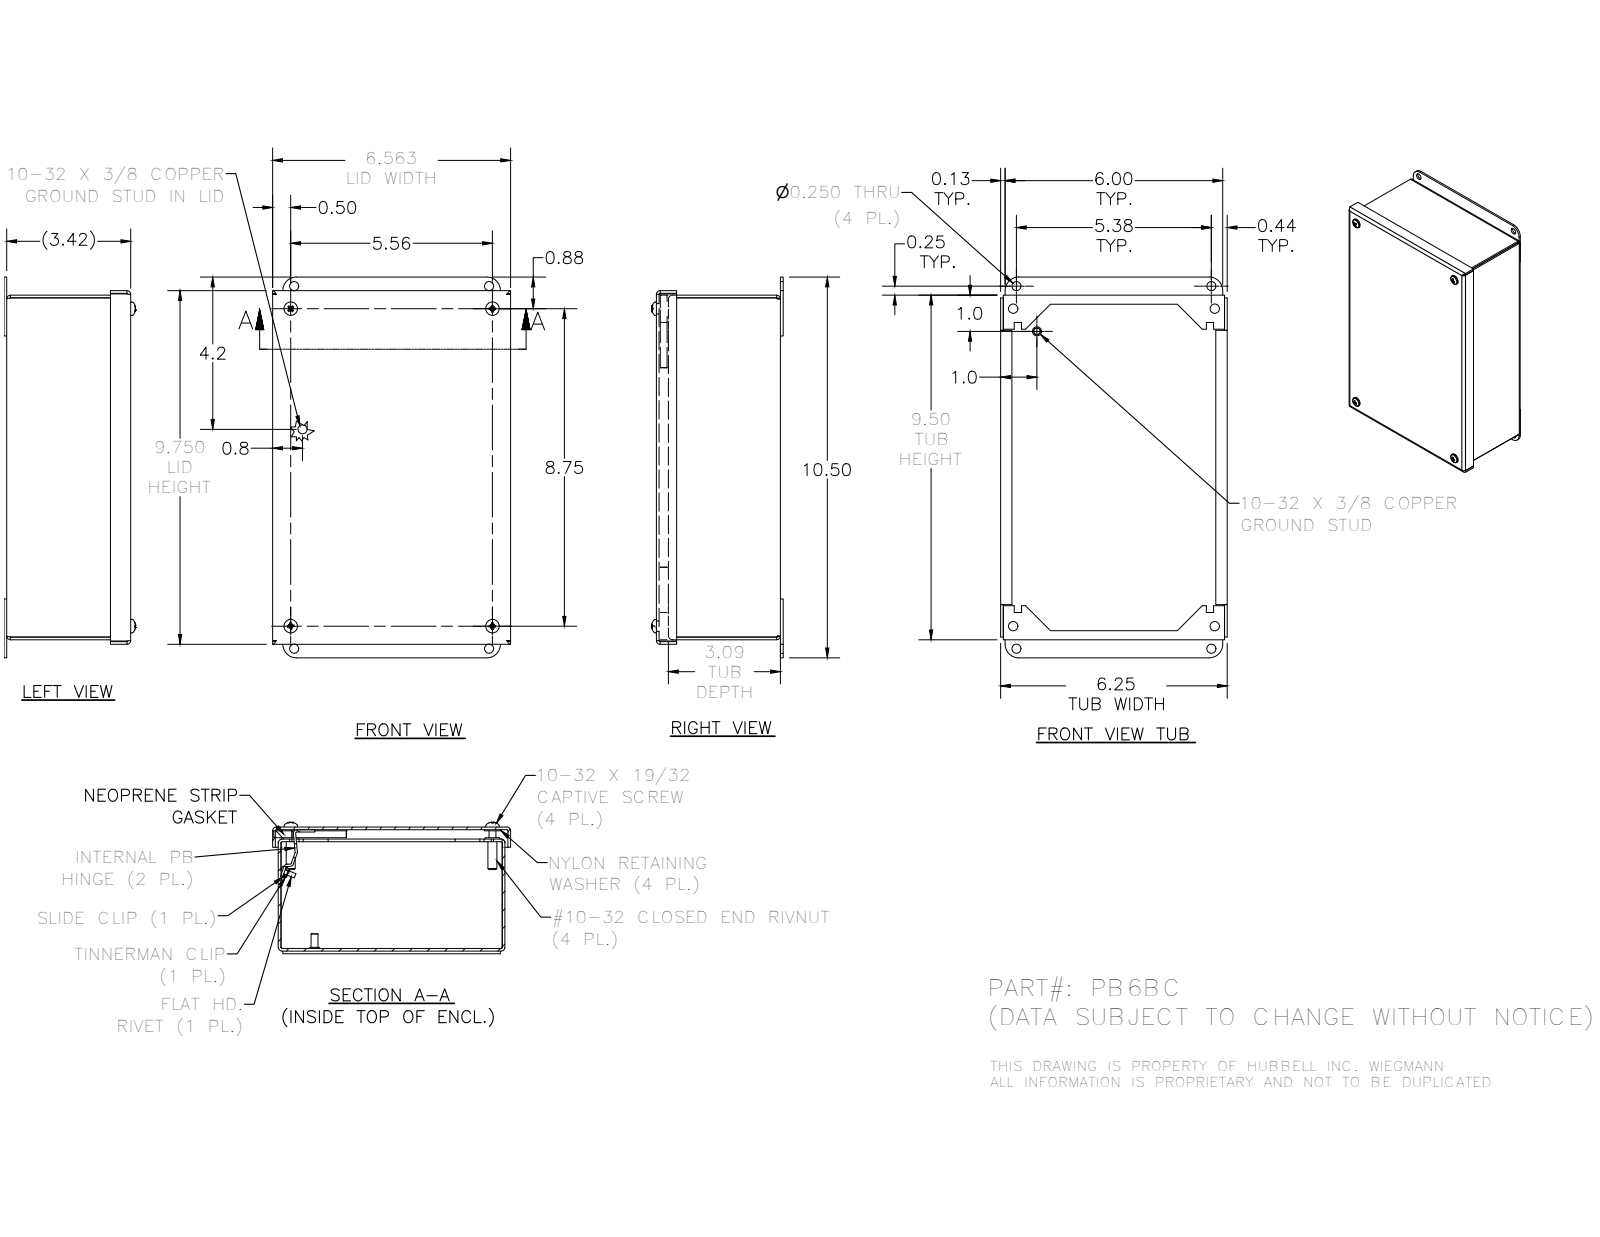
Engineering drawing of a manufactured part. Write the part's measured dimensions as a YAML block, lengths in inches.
part_name: "3285; 39077; 316243; 31817 (+8 more)"
step_written_by: "Autodesk Inventor 2016 (AUTOMOTIVE_DESIGN)"
units: inches
bodies: {solids: 25, faces: 599, planar: 355, cylindrical: 130, other: 114}
overall_size: [10.5, 6.563, 3.626]
volume: 20.27
surface_area: 554.6
round_holes:
  - {diameter: 0.156, count: 4}
  - {diameter: 0.196, count: 4}
  - {diameter: 0.25, count: 4}
  - {diameter: 0.257, count: 4}
  - {diameter: 0.278, count: 4}
  - {diameter: 0.281, count: 4}
  - {diameter: 0.14, count: 2}
  - {diameter: 0.313, count: 2}
round_bosses_or_shafts:
  - {diameter: 0.19, count: 6}
  - {diameter: 0.453, count: 4}
  - {diameter: 0.406, count: 4}
  - {diameter: 0.373, count: 4}
  - {diameter: 0.248, count: 4}
  - {diameter: 0.25, count: 3}
  - {diameter: 0.125, count: 1}
partial_cylinders:
  - {radius: 0.031, count: 12}
  - {radius: 0.105, count: 12}
  - {radius: 0.188, count: 6}
  - {radius: 0.089, count: 4}
  - {radius: 0.09, count: 4}
  - {radius: 0.375, count: 4}
  - {radius: 0.031, count: 3}
  - {radius: 0.063, count: 3}
face_to_face_distances: [0.074, 3.348, 3.422, 3.274, 6.176, 6.102, 6.25, 0.148, 3.496, 0.074]
hole_center_spacings: [8.75, 10.368, 0.632, 9.375, 9.376, 5.561, 10.368, 10.853]
